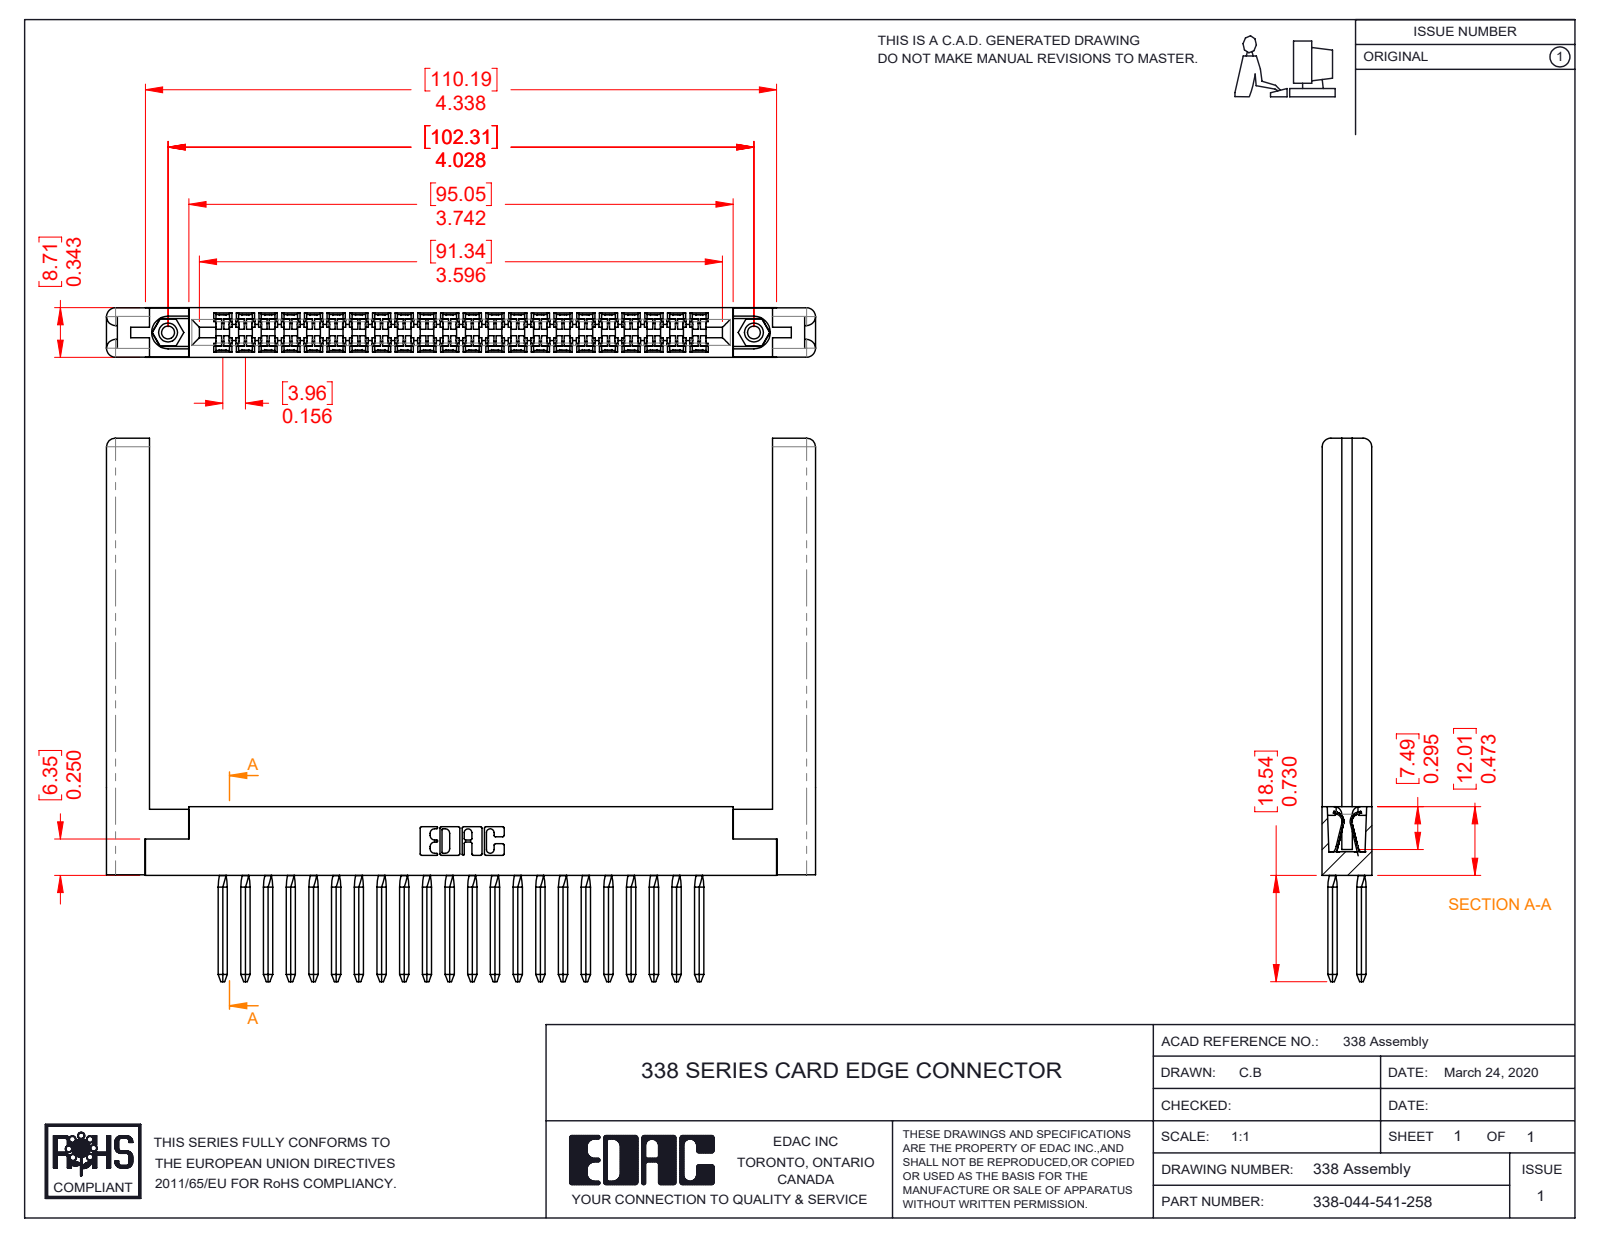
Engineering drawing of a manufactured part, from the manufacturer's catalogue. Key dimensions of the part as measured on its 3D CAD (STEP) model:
Part name (STEP PRODUCT): 307-220-058; 345-250-001_345-250-001-102; 338-290-001_541; 338-044-541-258 (+1 more)
STEP written by: SolidWorks 2016 (CONFIG_CONTROL_DESIGN)
Units: inches
Bodies: 49 solids, 3184 faces (2202 planar, 782 cylindrical, 200 other)
Overall size (bounding box): 4.874 × 3.735 × 0.343
Volume: 1.04 in³ · Surface area: 34.59 in²
Round holes (diameter × count): ⌀0.089 ×2, ⌀0.125 ×2, ⌀0.156 ×2
Round bosses / shafts (diameter × count): ⌀0.155 ×2
Partial cylindrical surfaces — rounded edges, fillets, slot ends (radius × count): R0.025 ×134, R0.008 ×44, R0.055 ×36, R0.067 ×36, R0.1 ×35, R0.01 ×22, R0.061 ×8, R0.007 ×6
Main face-to-face distances: 0.341, 0.343, 0.34, 0.136, 0.207, 0.134, 0.206, 0.22, 4.284, 0.071
Hole centre spacings: 4.028
